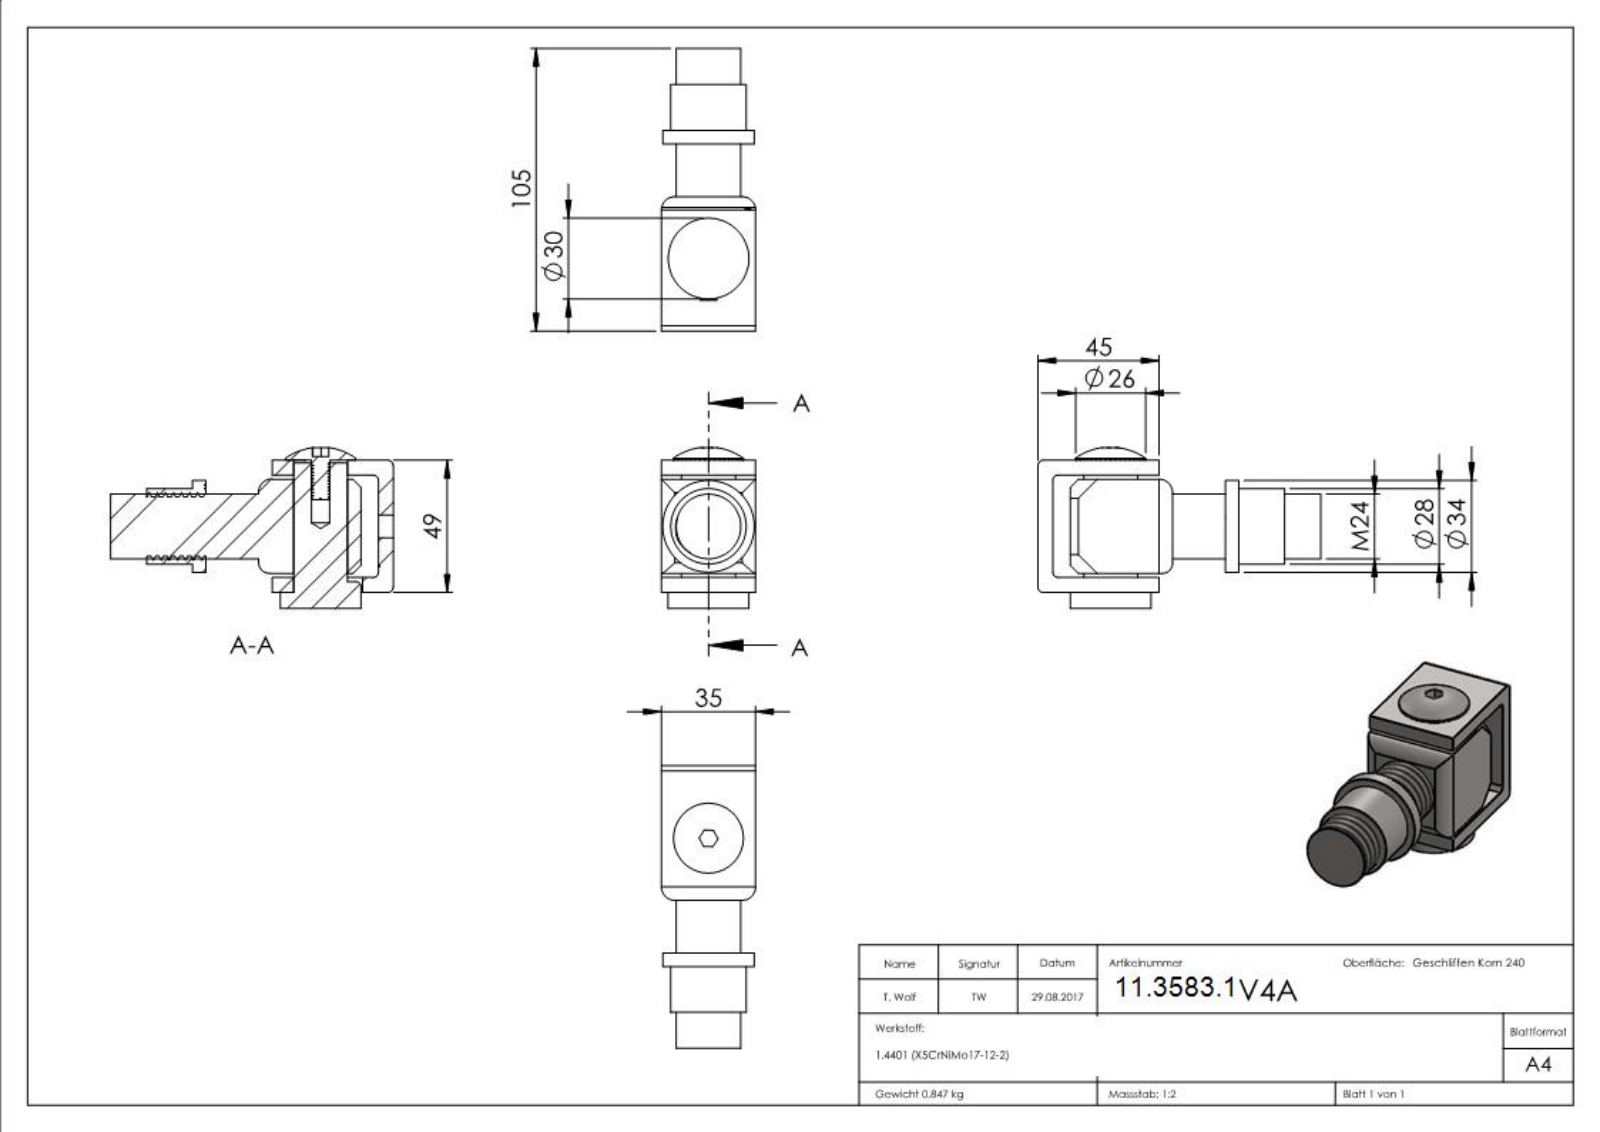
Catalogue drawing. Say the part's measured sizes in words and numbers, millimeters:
The part is named "120-M24-V4A; 120-M24-V4A Teil3; 120-M24-V4A Teil 2; 120-M24-V4A Teil4 (+3 more)". Its 3-D file was written by "SolidWorks 2018 (CONFIG_CONTROL_DESIGN)". It is 5 solids with 588 faces: 397 planar, 32 cylindrical and 159 other. Overall it measures 105 by 59.75 by 35 millimeters. Its volume is 105 865 cubic millimeters and its surface area 35 901 square millimeters. Round holes: 1 of diameter 6.8, 1 of diameter 8.5, 1 of diameter 20, 1 of diameter 22. Round bosses or shafts: 1 of diameter 34, 1 of diameter 30, 1 of diameter 28, 1 of diameter 26, 1 of diameter 24, 1 of diameter 7. Partial cylindrical surfaces (rounded edges, fillets, slot ends): 4 of radius 2, 3 of radius 5, 1 of radius 4. The main face-to-face distances are 5.5, 35, 43.5, 49, 1.5, 7, 42, 36.5, 38, 6.
